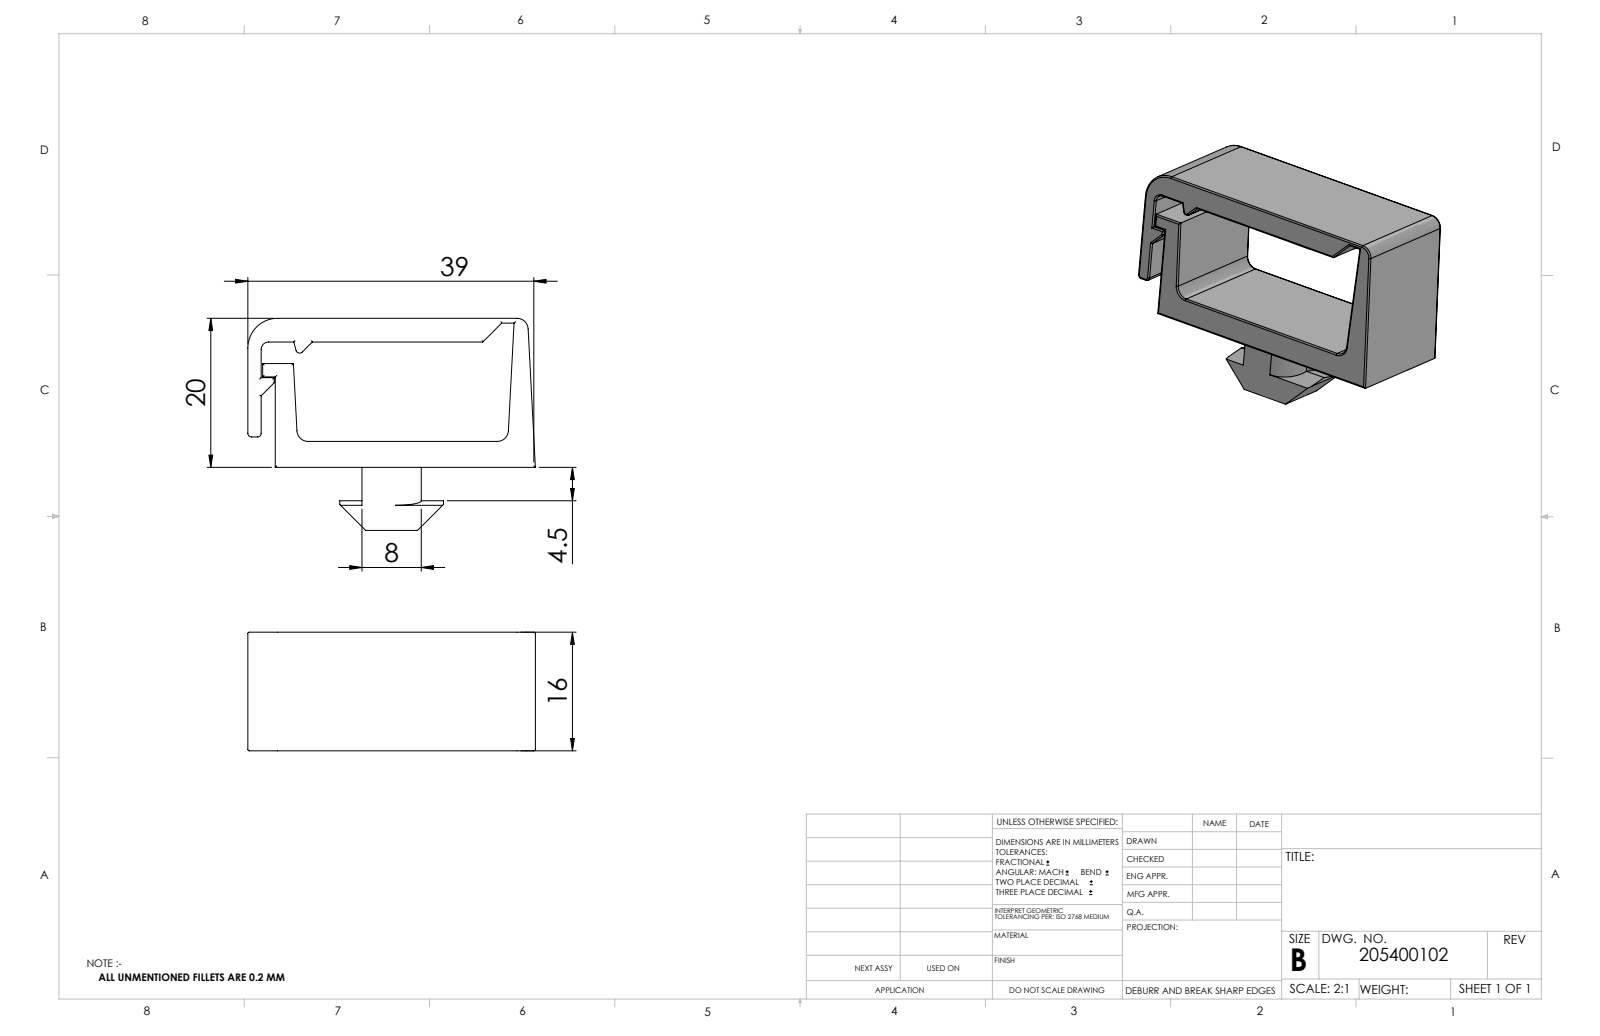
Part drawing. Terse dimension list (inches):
name: 205400102_c_1
written by: SolidWorks 2014 (CONFIG_CONTROL_DESIGN)
unit: in
bodies: 1 solid, 113 faces (38 planar, 57 cylindrical, 18 other)
size: 1.528 × 1.126 × 0.63
volume: 0.355 in³; area: 7.248 in²
rounds: 43× R0.008, 3× R0.02, 3× R0.059, 2× R0.138, 1× R0.039, 1× R0.157
face distances: 0.791, 0.528, 0.665, 0.126, 0.138, 0.654, 0.63, 0.146, 0.075, 0.071
